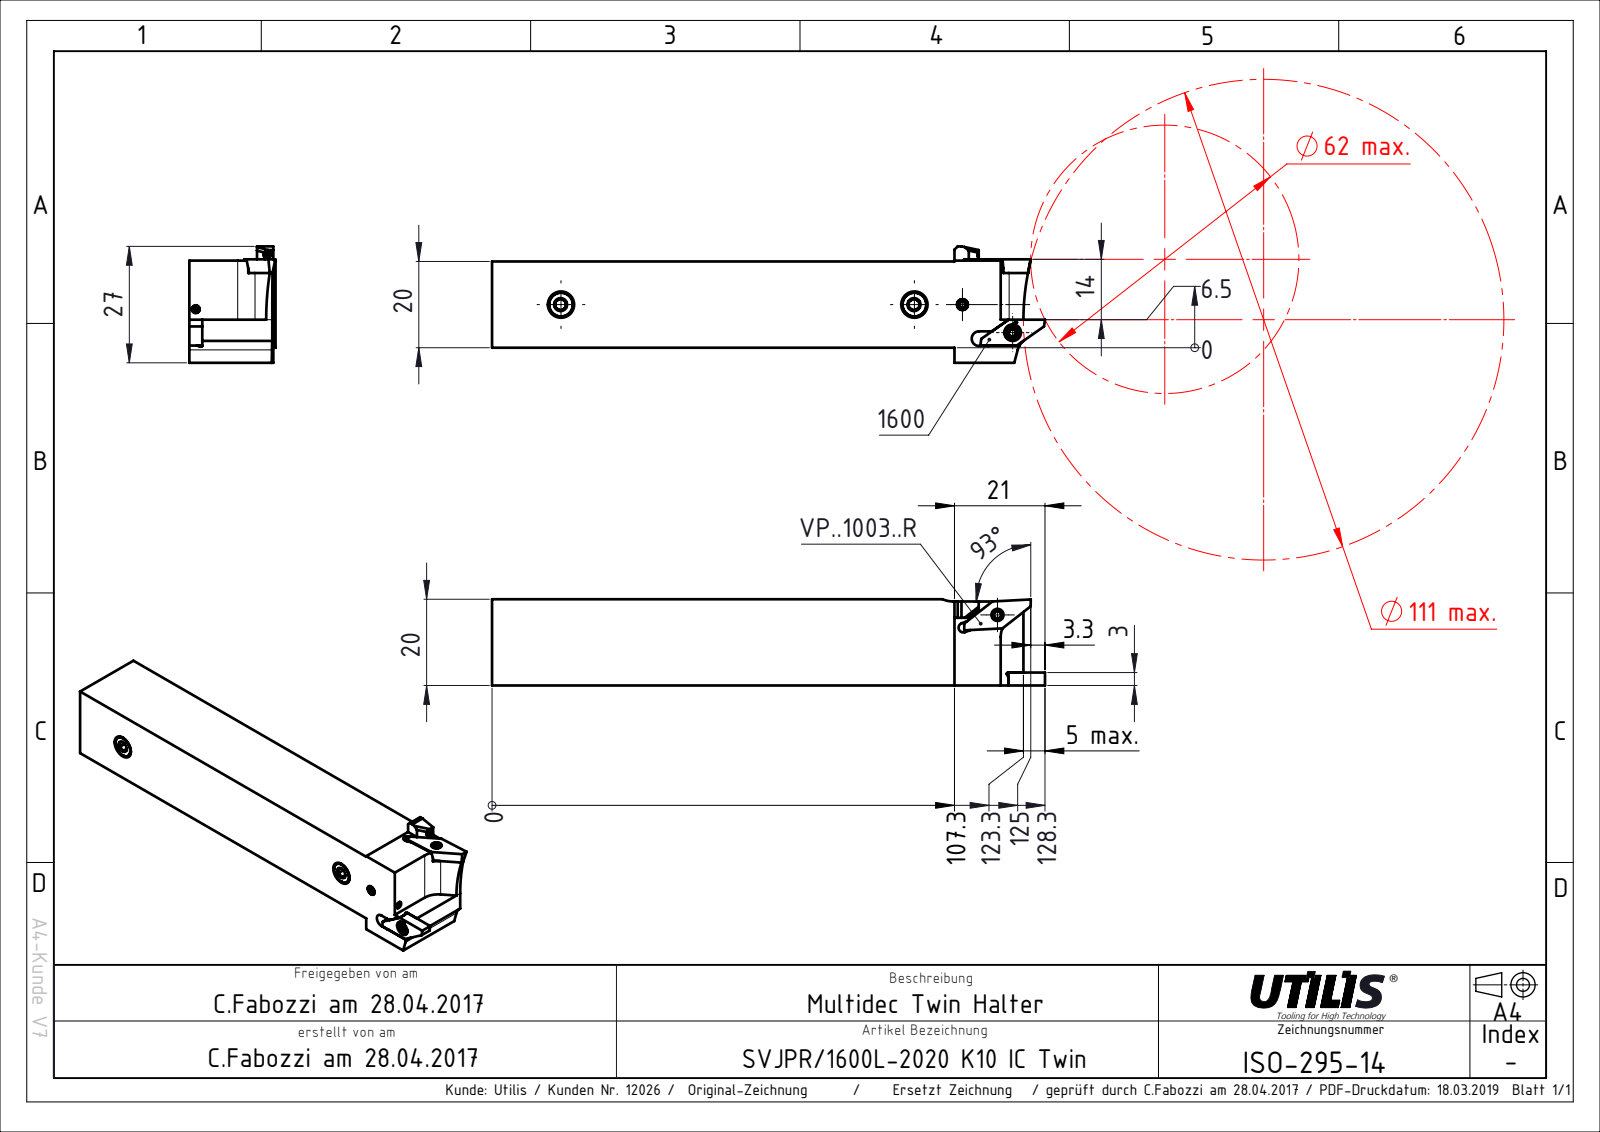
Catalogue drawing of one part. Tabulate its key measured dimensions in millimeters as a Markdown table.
| quantity | value |
| --- | --- |
| part name | ISO-295-14 |
| STEP written by | SolidWorks 2016 (AUTOMOTIVE_DESIGN) |
| units | millimeters |
| bodies | 1 solid, 81 faces (67 planar, 12 cylindrical, 2 other) |
| overall size | 128.3 × 27 × 20 |
| volume | 49 151 mm³ |
| surface area | 11 114 mm² |
| partial cylindrical surfaces (radius × count) | 0.25 × 2, 6.1 × 2, 0.5 × 1, 1.1 × 1, 1.55 × 1, 1.7 × 1, 4.1 × 1, 5.1 × 1 |
| main face-to-face distances | 20, 3.5, 23.5, 118.02, 23.7, 20.2, 10, 6.5, 13.5, 13.7 |
